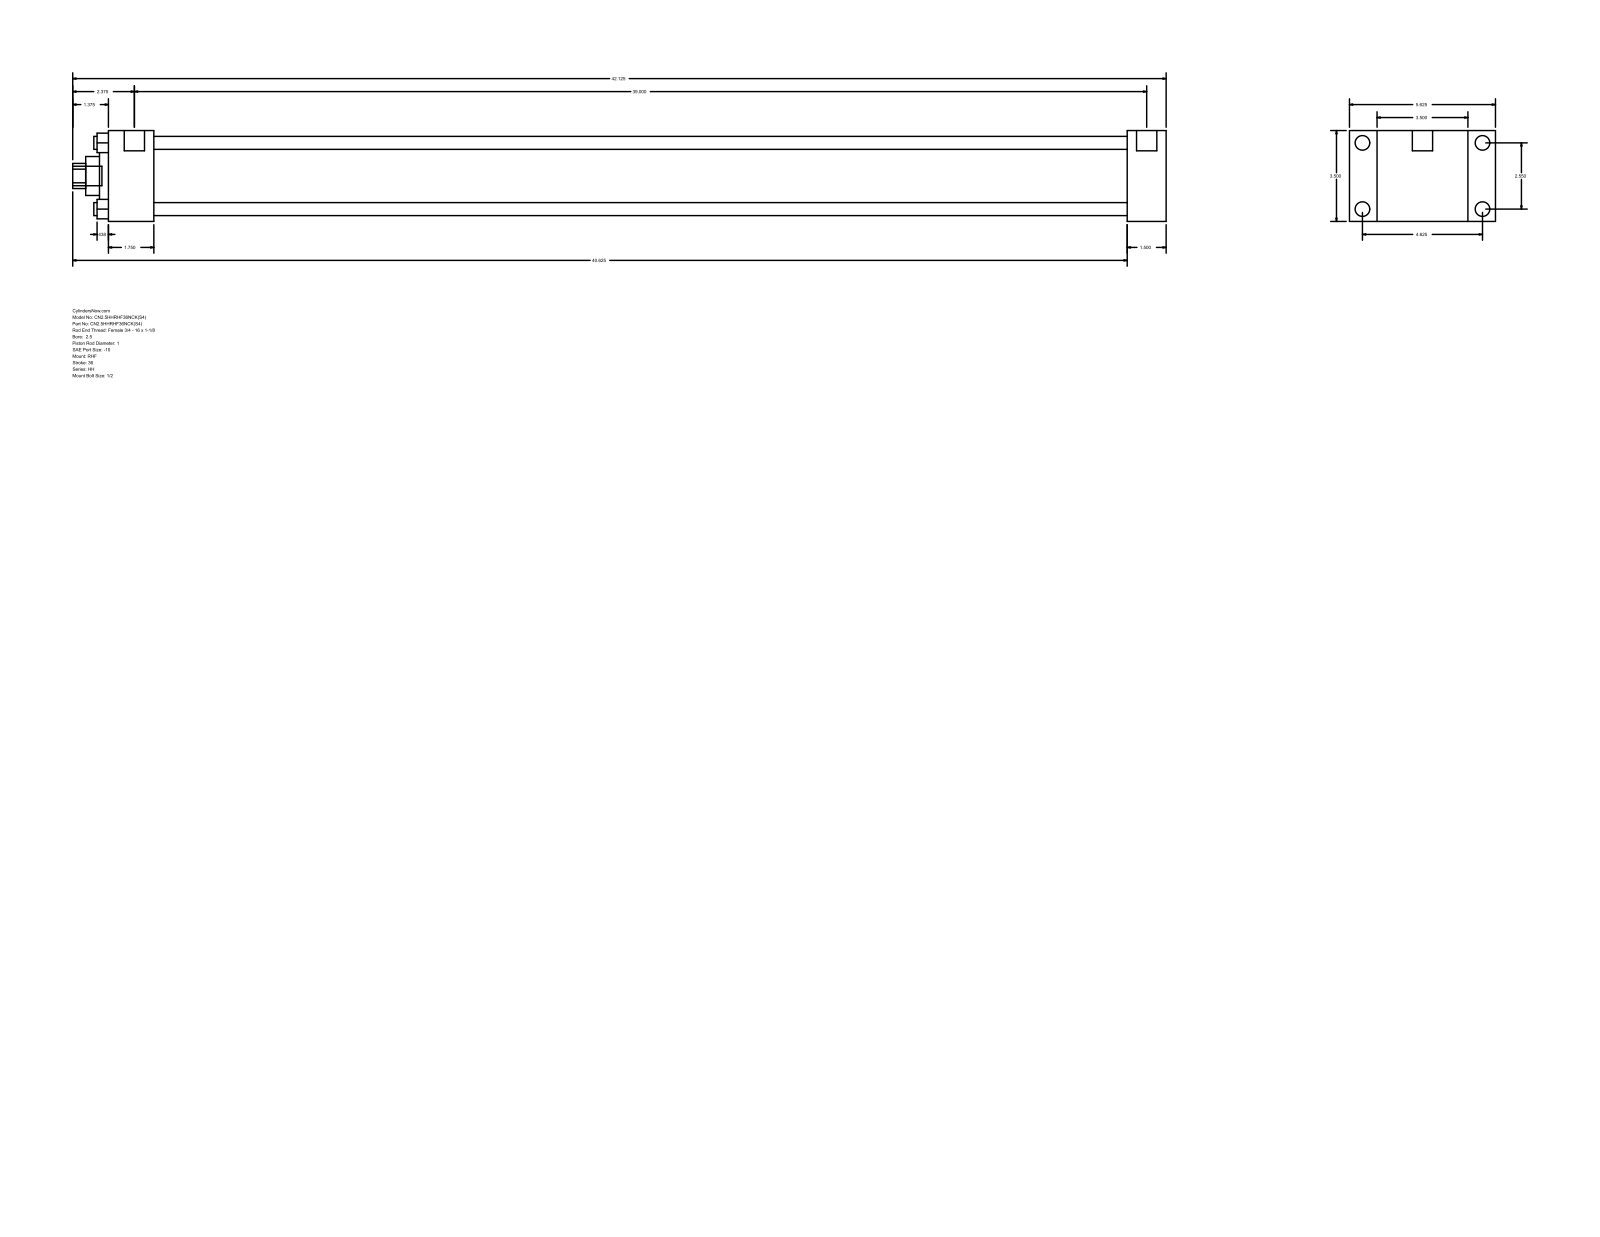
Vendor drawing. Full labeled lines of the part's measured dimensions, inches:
Part name (STEP PRODUCT): HH_RHF__0250_1
STEP written by: GSSL Pune (CONFIG_CONTROL_DESIGN)
Units: inches
Bodies: 0 solids, 90 faces (61 planar, 29 cylindrical, 0 other)
Overall size (bounding box): 42.125 × 5.625 × 3.5
Round holes (diameter × count): ⌀0.5 ×4, ⌀1 ×1, ⌀1.5 ×1, ⌀2.375 ×1, ⌀2.875 ×1
Round bosses / shafts (diameter × count): ⌀0.563 ×4, ⌀0.219 ×4, ⌀0.781 ×2, ⌀0.75 ×1
Partial cylindrical surfaces — rounded edges, fillets, slot ends (radius × count): R0.484 ×1
Main face-to-face distances: 3.5, 1.5, 1.063, 4.563, 39.25, 40.75, 5.625, 1.75, 37.5, 39
Hole centre spacings: 1.803, 2.55, 3.606
